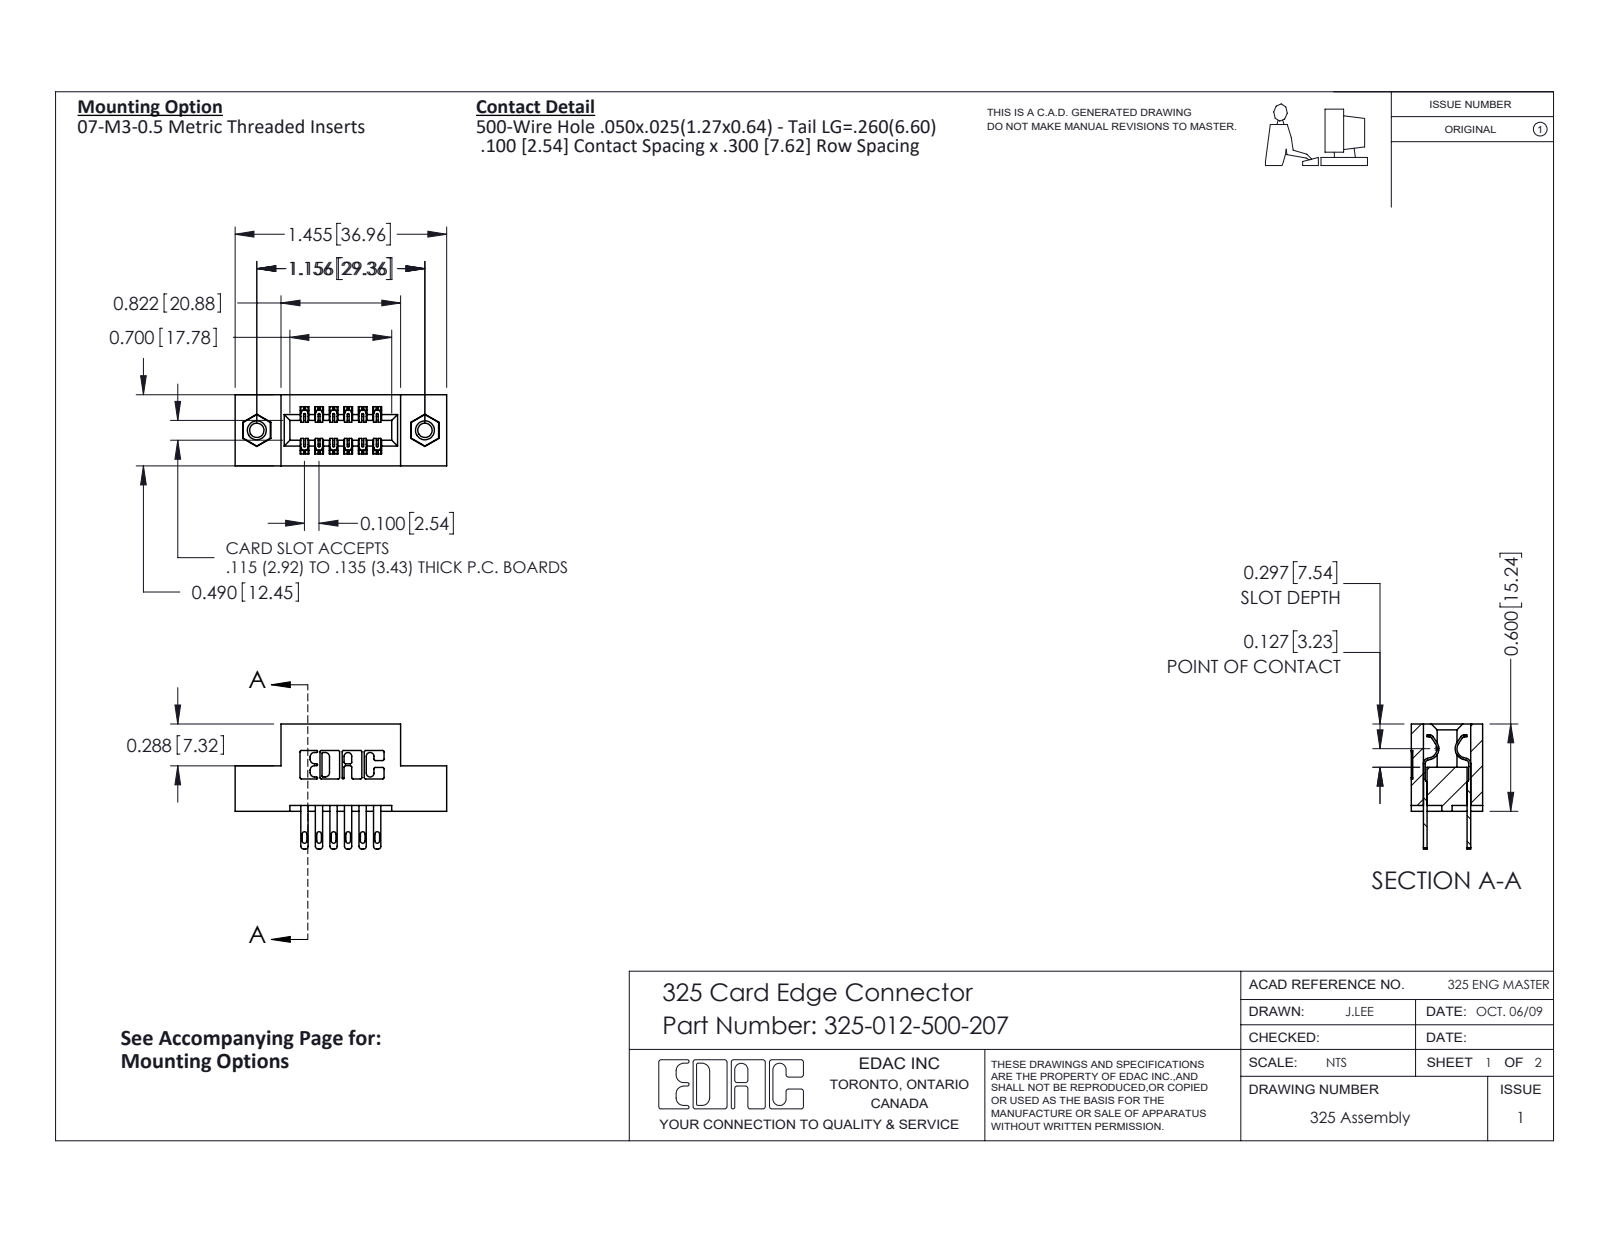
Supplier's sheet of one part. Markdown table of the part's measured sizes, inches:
| quantity | value |
| --- | --- |
| part name | 325 Part_TI; 325-012-500-207; 325-292-001_325-293-100; 345-250-001_345-250-005-103 |
| STEP written by | SolidWorks 2016 (CONFIG_CONTROL_DESIGN) |
| units | inches |
| bodies | 15 solids, 750 faces (462 planar, 272 cylindrical, 16 other) |
| overall size | 1.455 × 0.86 × 0.49 |
| volume | 0.273 in³ |
| surface area | 7.3 in² |
| round holes (diameter × count) | 0.098 × 2, 0.125 × 2, 0.16 × 2 |
| round bosses / shafts (diameter × count) | 0.155 × 2 |
| partial cylindrical surfaces (radius × count) | 0.01 × 22, 0.006 × 18, 0.016 × 12, 0.02 × 12, 0.007 × 6, 0.031 × 6, 0.026 × 3, 0.014 × 2 |
| main face-to-face distances | 0.3, 0.083, 0.407, 0.1, 0.04, 0.49, 0.2, 0.107, 0.383, 0.025 |
| hole center spacings | 1.156 |
